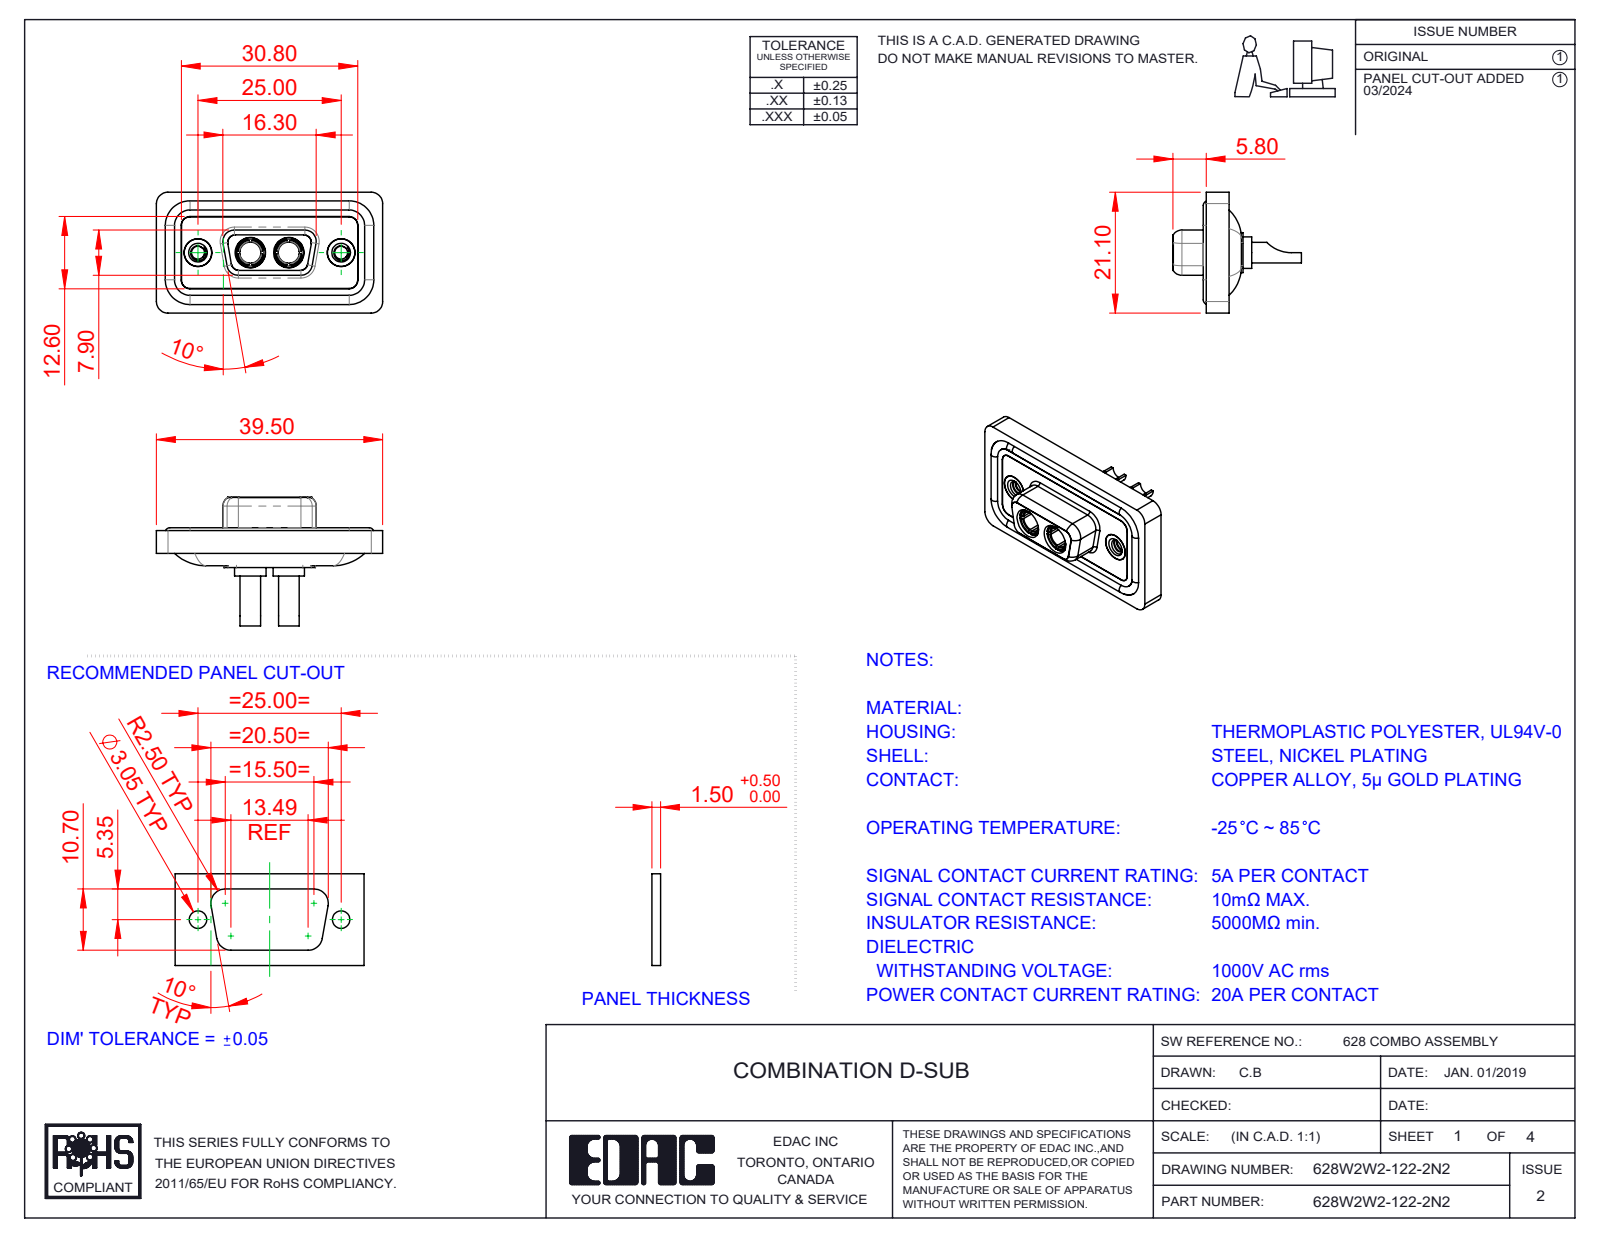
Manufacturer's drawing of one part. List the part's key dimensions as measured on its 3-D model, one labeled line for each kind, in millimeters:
Part name (STEP PRODUCT): 628Combo Housing_2W2; 628Combo Threaded Rivet_2; 628Combo Waterproof Housing_09 Contacts; 628W2W2-122-2N2 (+3 more)
STEP written by: SolidWorks 2023 (CONFIG_CONTROL_DESIGN)
Units: millimetres
Bodies: 11 solids, 546 faces (169 planar, 240 cylindrical, 137 other)
Overall size (bounding box): 39.5 × 22.45 × 21.1
Volume: 4 738 mm³ · Surface area: 7 801 mm²
Round holes (diameter × count): ⌀4.85 ×4, ⌀2.26 ×2, ⌀2.7 ×2, ⌀3.7 ×2, ⌀4 ×2, ⌀4.05 ×2, ⌀5 ×2, ⌀5.3 ×2
Round bosses / shafts (diameter × count): ⌀1.6 ×4, ⌀5.5 ×2, ⌀5.2 ×2, ⌀4.96 ×2, ⌀4.95 ×2, ⌀4.8 ×2, ⌀4.75 ×2, ⌀3.75 ×2
Partial cylindrical surfaces — rounded edges, fillets, slot ends (radius × count): R1.5 ×22, R2 ×18, R1.35 ×8, R1.6 ×8, R0.25 ×4, R0.5 ×4, R0.6 ×4, R0.65 ×4
Main face-to-face distances: 0.4, 1.8, 1.1, 2.9, 0.5, 1.6, 5.65, 7.45, 5.35, 1.5
Hole centre spacings: 9.14, 15.86, 6.72, 25
